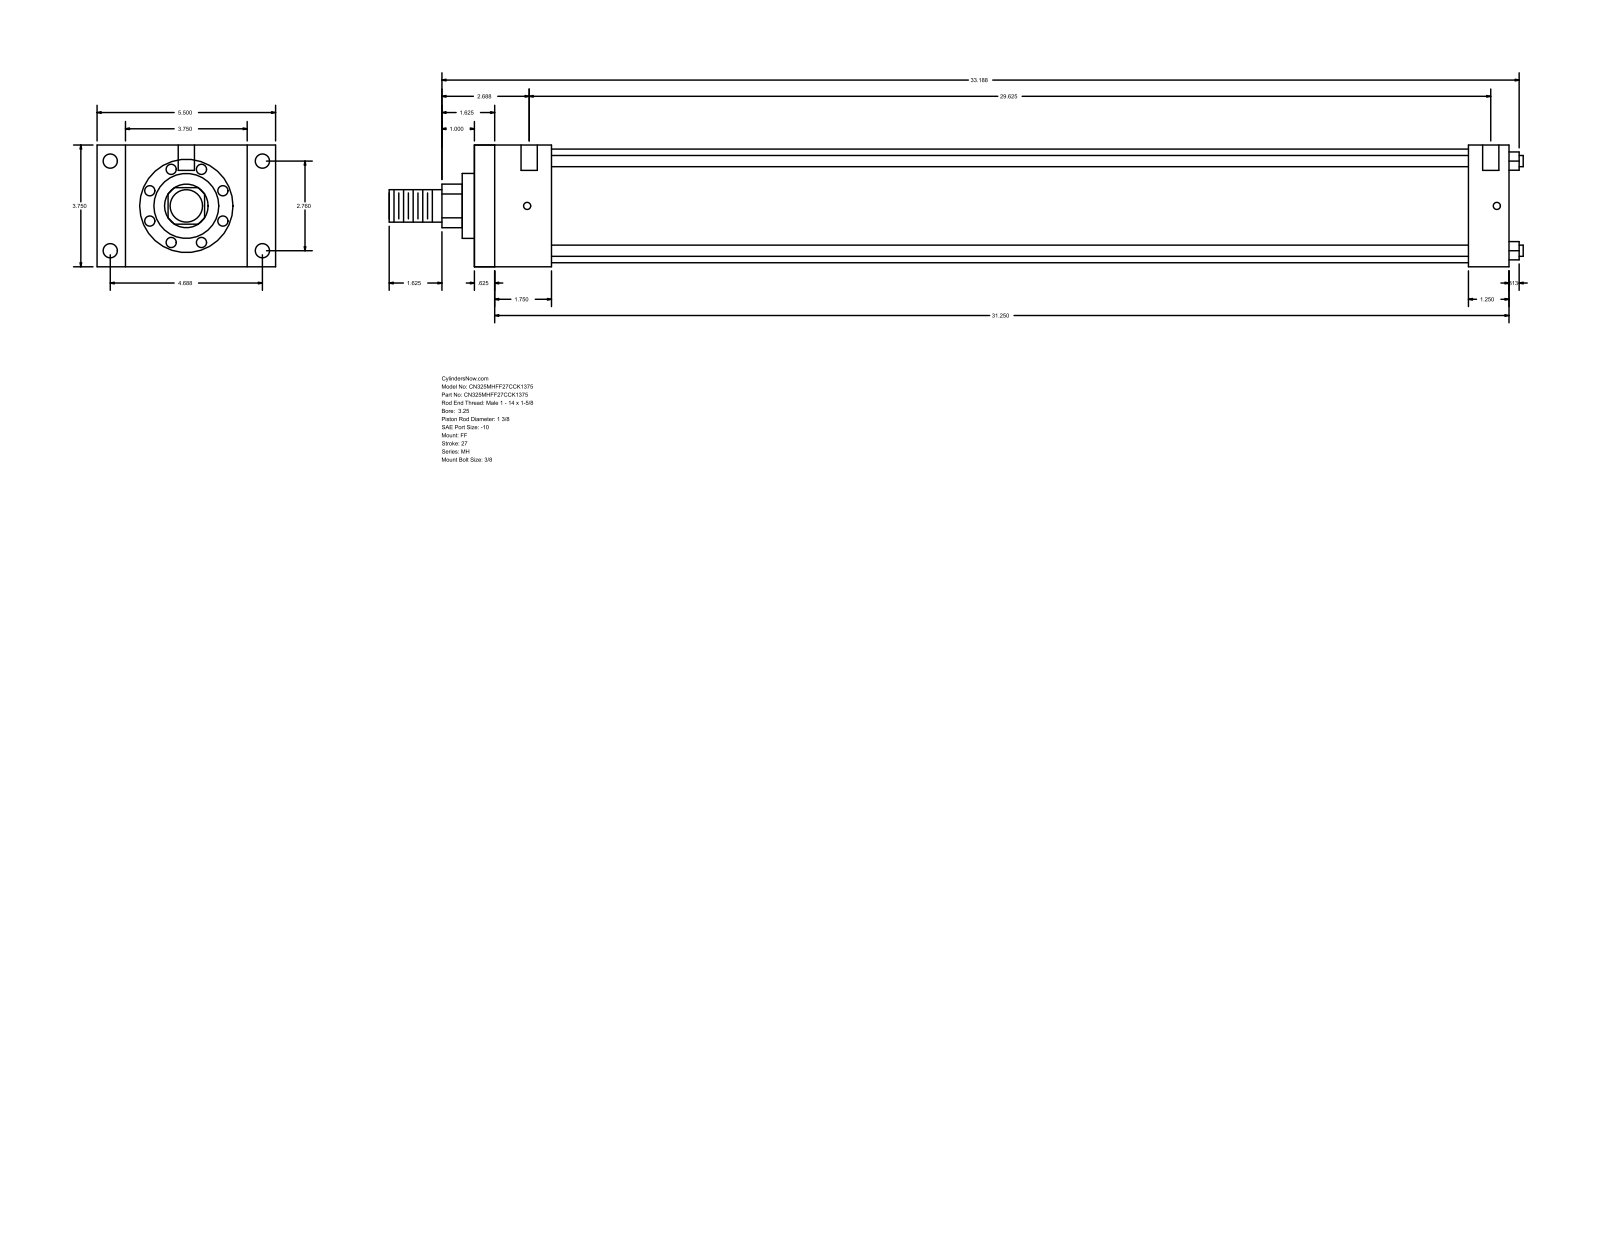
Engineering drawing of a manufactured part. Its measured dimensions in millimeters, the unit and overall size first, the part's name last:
Units: millimetres
Overall size (bounding box): 887.41 × 139.7 × 95.25
Round holes (diameter × count): ⌀5.56 ×4, ⌀11.13 ×4, ⌀12.7 ×2
Round bosses / shafts (diameter × count): ⌀8.76 ×4, ⌀88.9 ×1, ⌀50.8 ×1, ⌀34.92 ×1, ⌀25.4 ×1
Partial cylindrical surfaces — rounded edges, fillets, slot ends (radius × count): R17.06 ×1
Main face-to-face distances: 95.24, 809.62, 15.87, 793.75, 22.23, 117.47, 777.87, 762, 31.75, 60.32
Hole centre spacings: 70.1, 119.06, 138.16, 758.83, 1.59, 4.76, 752.48, 754.07
Bodies: 0 solids, 92 faces (64 planar, 28 cylindrical, 0 other)
Part name (STEP PRODUCT): MH_FF__0325_1.375
STEP written by: GSSL Pune (CONFIG_CONTROL_DESIGN)
